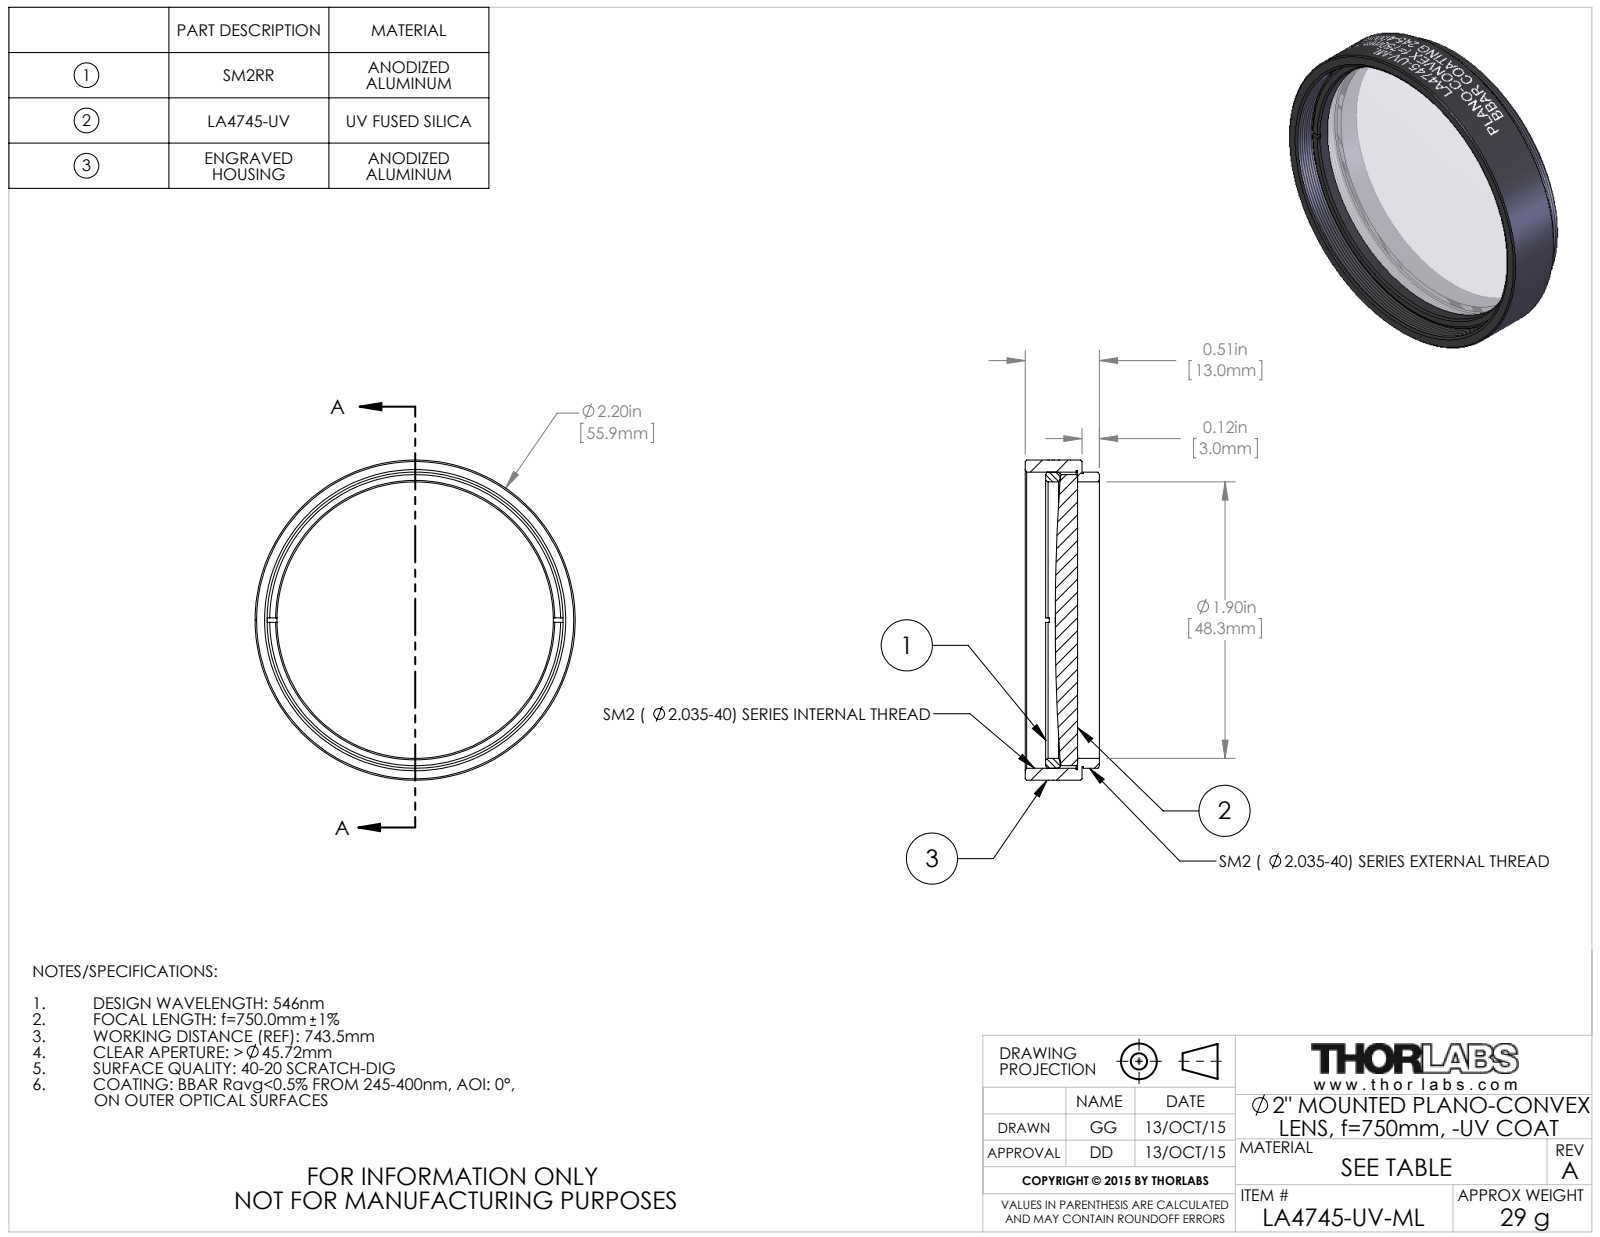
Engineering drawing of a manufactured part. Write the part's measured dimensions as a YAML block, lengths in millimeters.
part_name: "TTN039383-E0W"
step_written_by: "SolidWorks 2014 (CONFIG_CONTROL_DESIGN)"
units: millimeters
bodies: {solids: 3, faces: 147, planar: 16, cylindrical: 107, other: 24}
overall_size: [55.88, 55.88, 12.95]
volume: 12124
surface_area: 11306
round_holes:
  - {diameter: 48.26, count: 1}
  - {diameter: 52.2, count: 1}
round_bosses_or_shafts:
  - {diameter: 55.88, count: 1}
  - {diameter: 51.69, count: 1}
  - {diameter: 51.18, count: 1}
  - {diameter: 50.8, count: 1}
face_to_face_distances: [0.76, 9.91, 9.15, 3.05, 3.81, 12.96, 6.87, 3.82, 3.06, 6.09]
